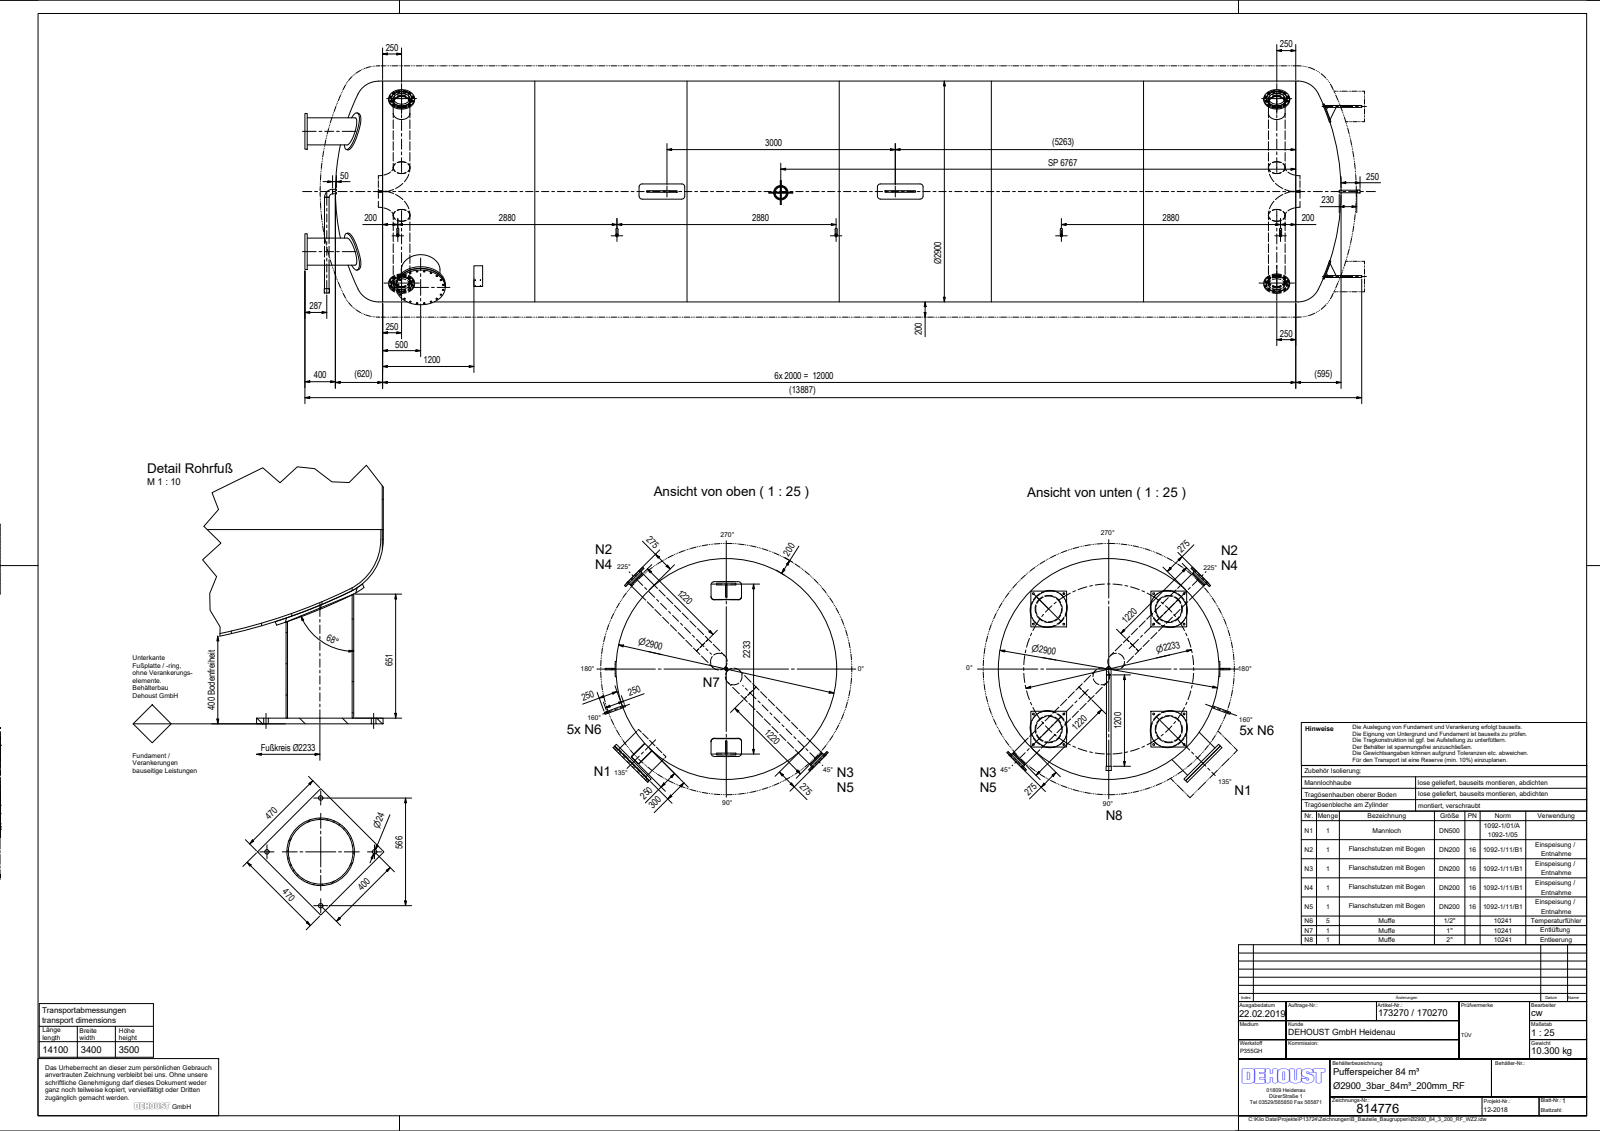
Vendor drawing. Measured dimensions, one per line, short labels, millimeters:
name: Ø2900_84_3_200_RF_WZ2; Klöpper_Gew_Ø2900_7,5; Klöpper_Gew_Ø2900_13,0; Zyl_Ø2900_6x12000_2019 (+8 more)
written by: Autodesk Inventor 2019 (AUTOMOTIVE_DESIGN)
unit: mm
bodies: 58 solids, 457 faces (176 planar, 231 cylindrical, 50 other)
size: 13886.69 × 3051.99 × 2937.4
volume: 1 229 000 000 mm³; area: 278 700 000 mm²
holes: 80× ⌀22, 16× ⌀24, 5× ⌀18.63, 5× ⌀21.7, 5× ⌀26.9, 4× ⌀5.8, 4× ⌀204.9, 4× ⌀207.3, 4× ⌀219.1, 4× ⌀339.6, 2× ⌀52.3, 2× ⌀72
bosses: 8× ⌀219.1, 5× ⌀26.9, 5× ⌀26.4, 4× ⌀500, 4× ⌀355.6, 4× ⌀340, 4× ⌀268, 1× ⌀2900
rounds: 8× R40, 8× R42, 2× R5, 2× R10, 2× R72, 1× R125, 1× R1462
face distances: 30, 600, 6646.24, 7394.24, 6616.24, 7364.24, 748, 27.99, 5626, 6374
hole spacings: 300, 147.5, 185.41, 93.86, 352.67, 592.61, 2880, 485.41
